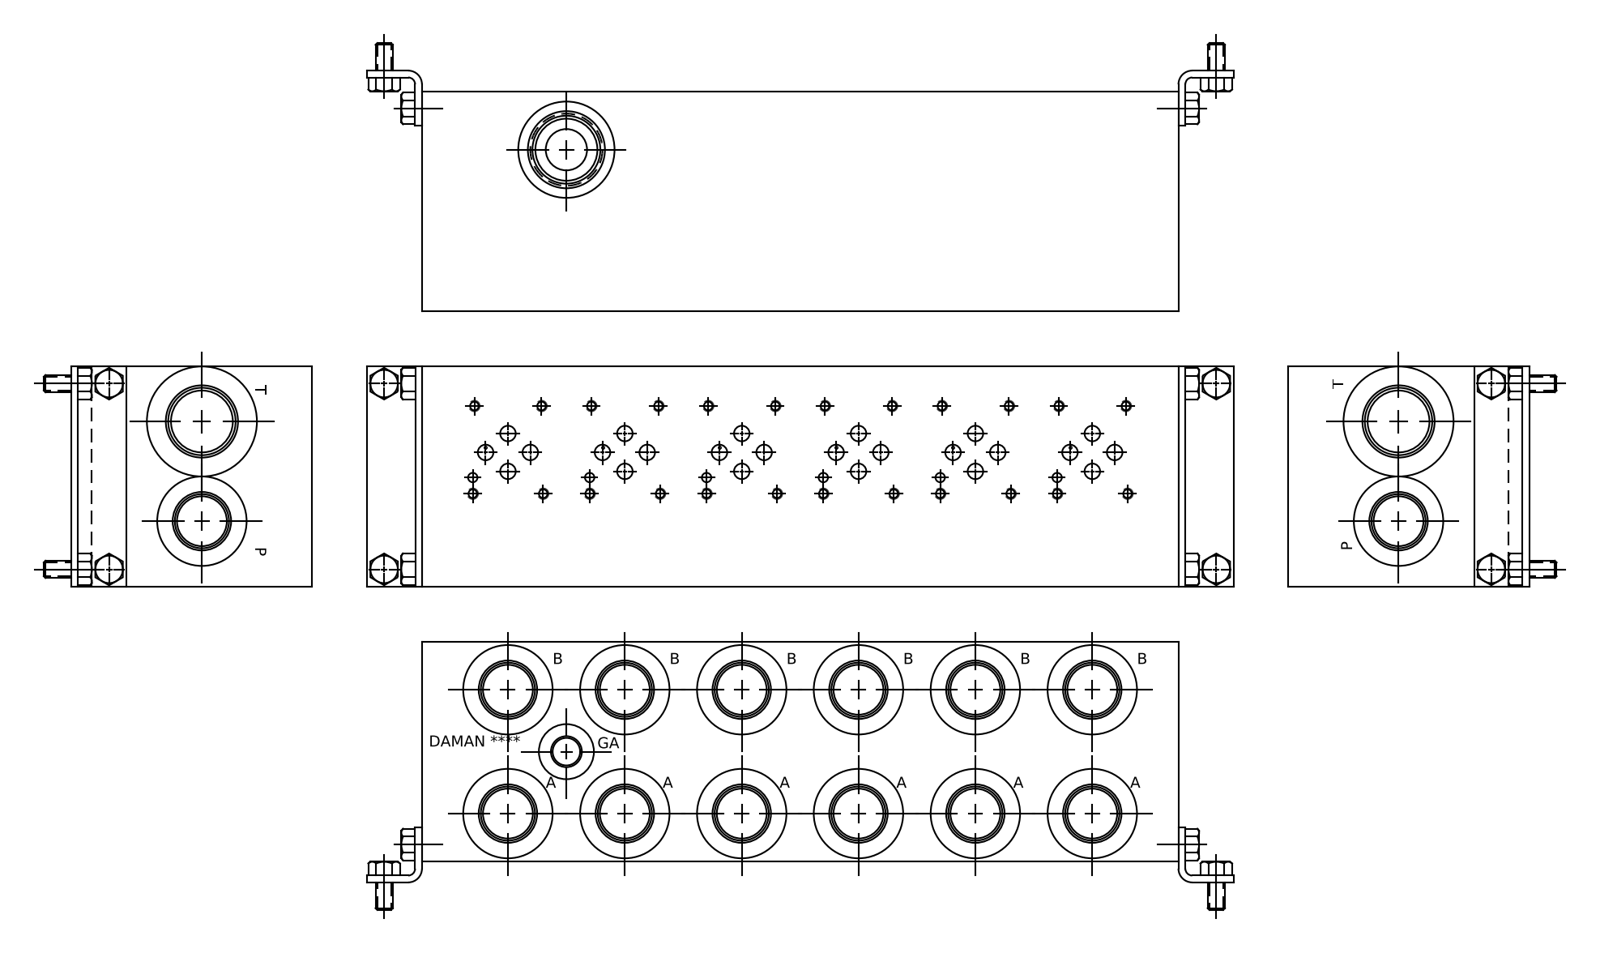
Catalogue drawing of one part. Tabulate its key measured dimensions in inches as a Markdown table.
| quantity | value |
| --- | --- |
| part name | Part_AD03HP062S_C_3D |
| STEP written by | Autodesk Inventor 2020 (AUTOMOTIVE_DESIGN) |
| units | inches |
| bodies | 1 solid, 1075 faces (509 planar, 184 cylindrical, 382 other) |
| overall size | 13.75 × 4 × 4 |
| volume | 197.5 in³ |
| surface area | 342.6 in² |
| round holes (diameter × count) | 0.149 × 24, 0.19 × 24, 0.25 × 18, 0.906 × 13, 0.981 × 13, 1.08 × 13, 1.655 × 13, 1.063 × 12, 0.156 × 6, 0.281 × 6, 0.422 × 6, 0.257 × 2 |
| main face-to-face distances | 4, 0.031, 3.969, 13.75, 13.719, 13.688, 0.781, 0.75, 3.219, 3.875 |
| hole center spacings | 4.25, 2.125, 2.125, 8.5, 6.375, 0.532, 0.533, 3.095 |
